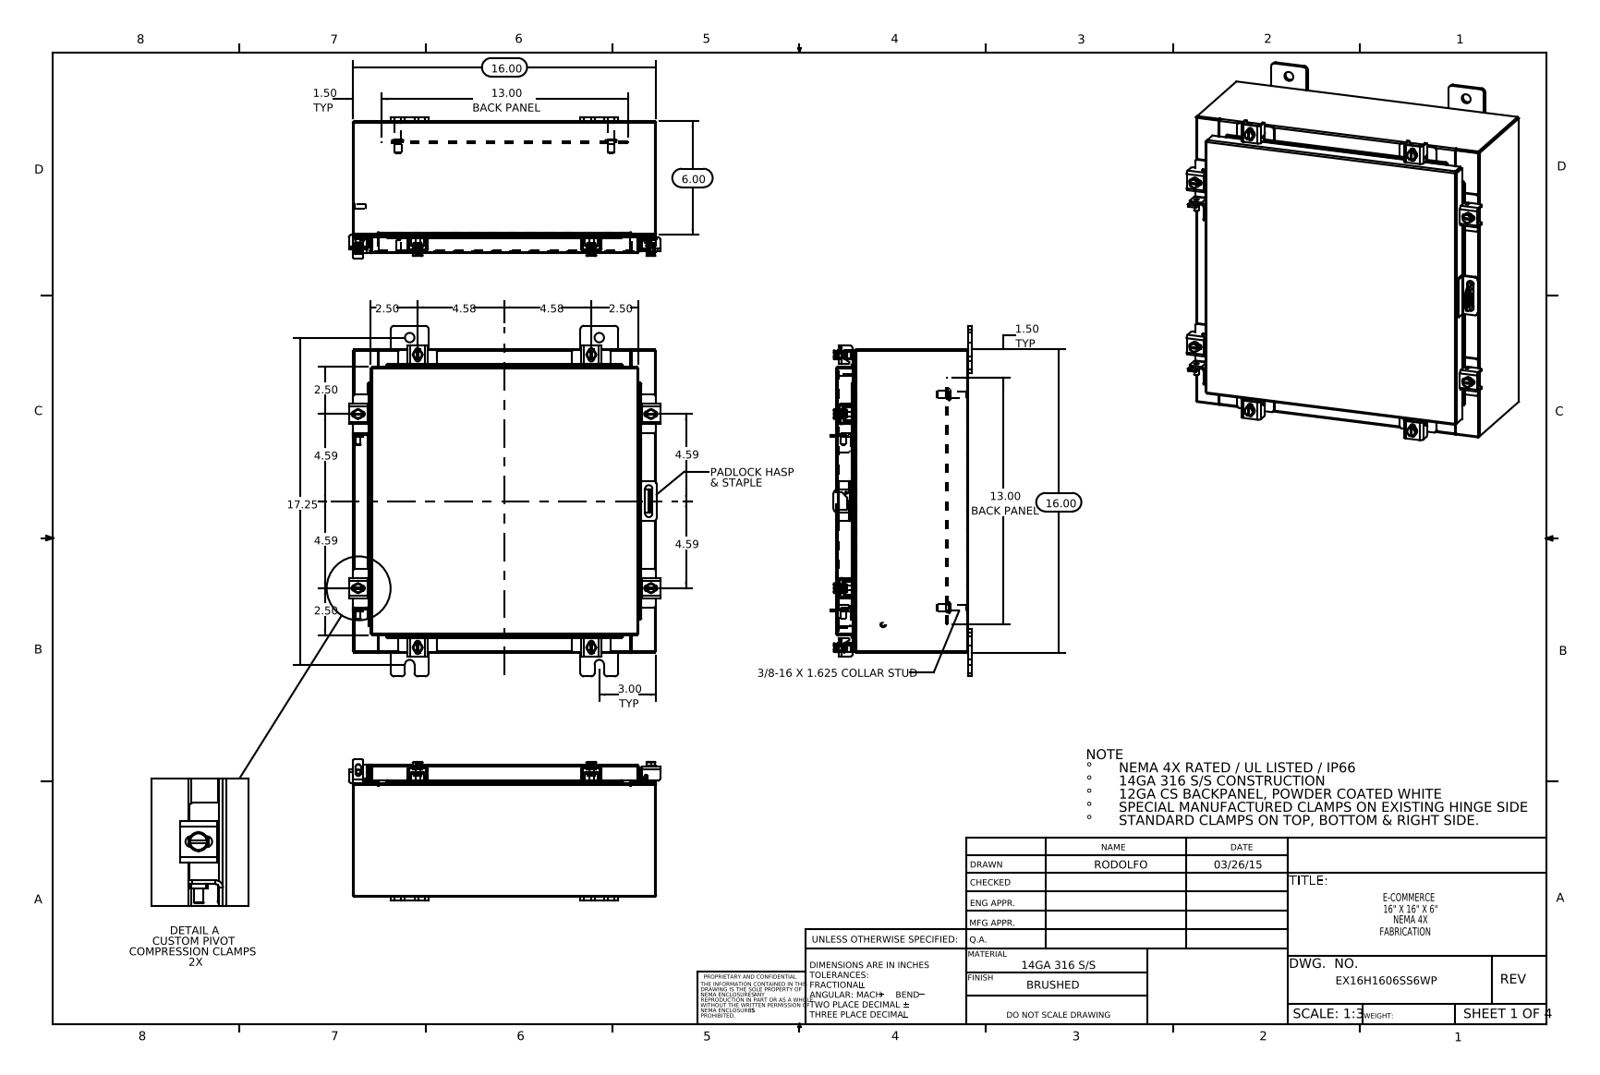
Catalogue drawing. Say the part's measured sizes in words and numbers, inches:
The part is named "Special Clamp Assembly; EX16H1606SS6WP Bottom; 22101002_RTP29; EX16H1606SS6WP Mounting Studs (+8 more)". Its 3-D file was written by "SolidWorks 2014 (CONFIG_CONTROL_DESIGN)". It is 61 solids with 1534 faces: 823 planar, 583 cylindrical and 128 other. Overall it measures 18.5 by 16.421 by 7.453 inches. Its volume is 101.7 cubic inches and its surface area 2 558 square inches. Round holes: 8 of diameter 0.213, 8 of diameter 0.26, 8 of diameter 0.5, 1 of diameter 0.125, 1 of diameter 0.25. Round bosses or shafts: 8 of diameter 0.5, 8 of diameter 0.25, 6 of diameter 0.399, 4 of diameter 0.625, 4 of diameter 0.375, 4 of diameter 0.33, 2 of diameter 0.315, 2 of diameter 0.236. Partial cylindrical surfaces (rounded edges, fillets, slot ends): 36 of radius 0.06, 24 of radius 0.19, 22 of radius 0.013, 22 of radius 0.088, 16 of radius 0.1, 16 of radius 0.141, 14 of radius 0.09, 14 of radius 0.12. The main face-to-face distances are 0.075, 6.9, 15.925, 6.975, 6.826, 15.85, 16, 1, 1.075, 5.826. The hole center spacings are 2.347, 4.44, 10.433, 12.696, 12.715, 13.392, 15.451, 16.803.
